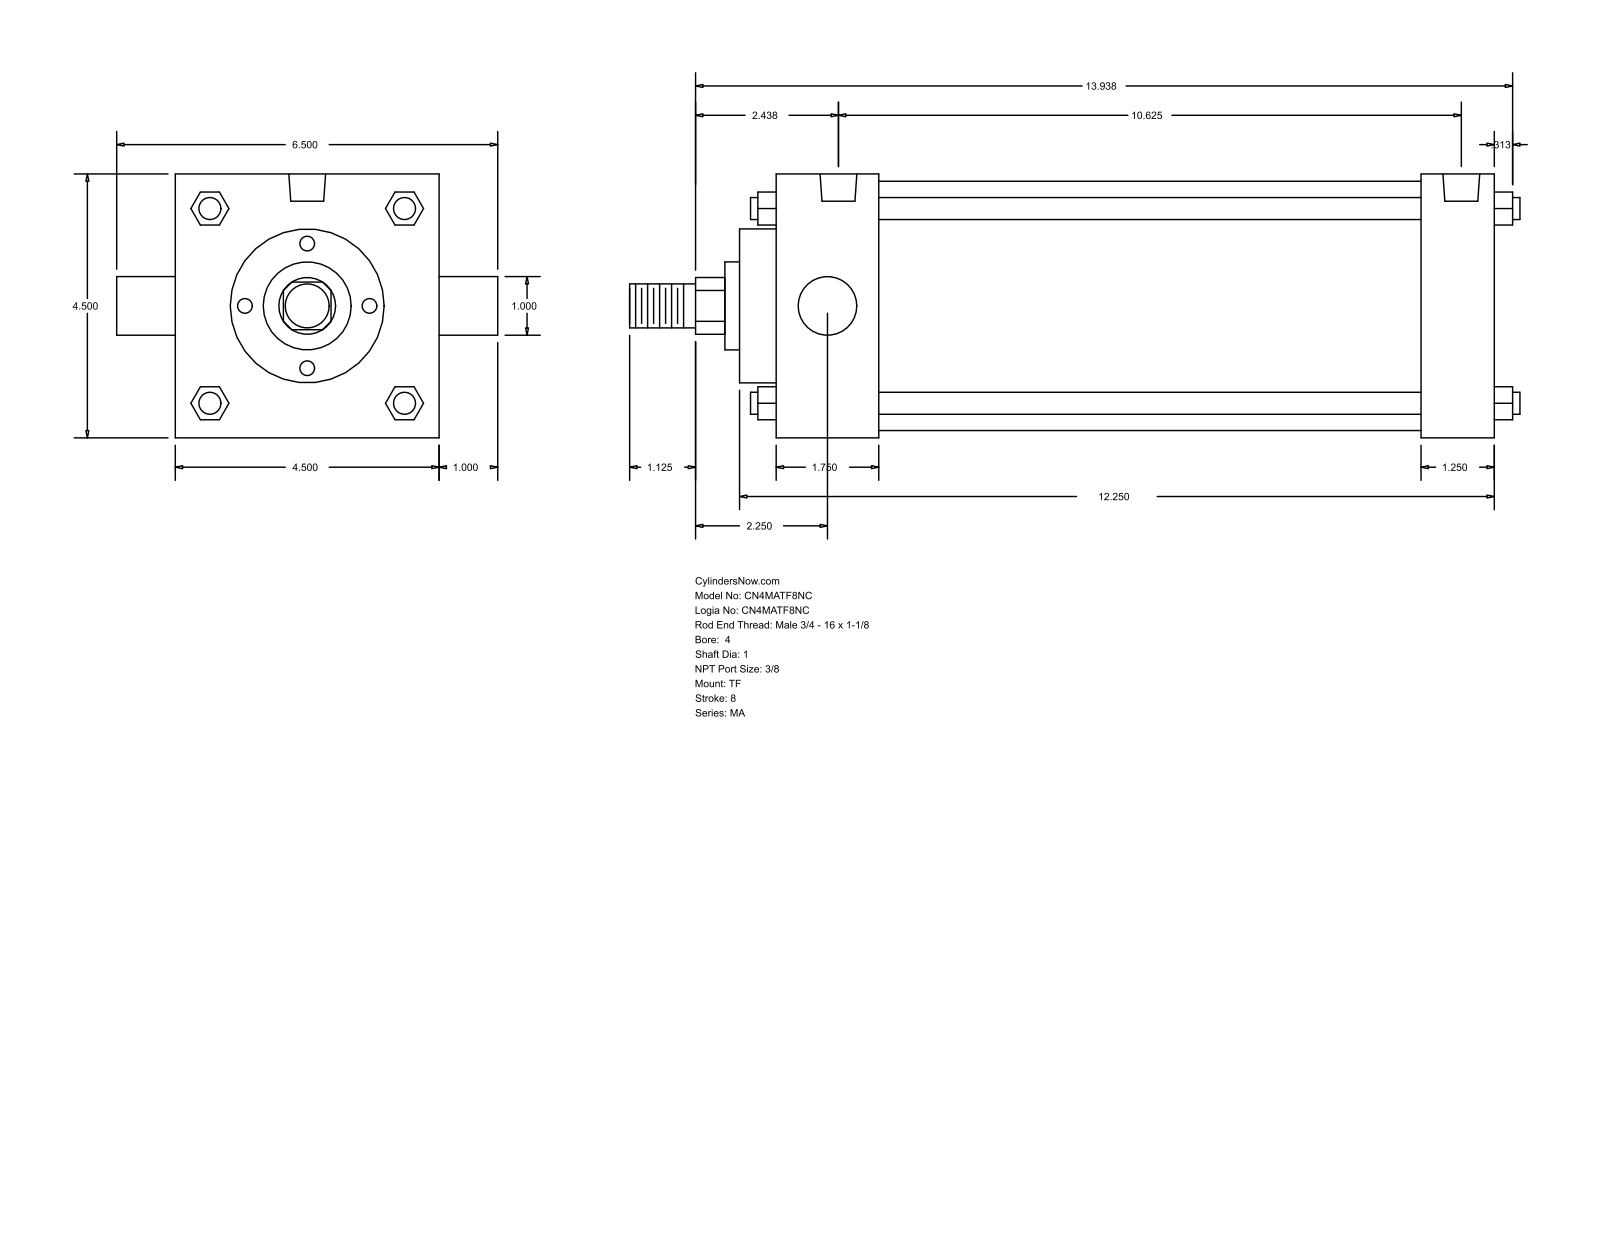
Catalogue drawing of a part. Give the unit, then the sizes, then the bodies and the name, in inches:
Units: inches
Overall size (bounding box): 15.187 × 6.5 × 4.5
Round holes (diameter × count): ⌀0.437 ×3, ⌀0.627 ×2
Round bosses / shafts (diameter × count): ⌀0.375 ×4, ⌀1 ×2, ⌀4.25 ×1, ⌀2.625 ×1, ⌀1.5 ×1, ⌀0.75 ×1
Partial cylindrical surfaces — rounded edges, fillets, slot ends (radius × count): R0.484 ×1
Main face-to-face distances: 4.5, 12.25, 11, 1.25, 1.75, 9.25, 10.5, 12.875, 0.625, 2.375
Hole centre spacings: 0.187, 0.188, 10.25, 10.437, 10.438, 10.625
Bodies: 0 solids, 122 faces (93 planar, 29 cylindrical, 0 other)
Part name (STEP PRODUCT): MA_TF__0400_1
STEP written by: GSSL Pune (CONFIG_CONTROL_DESIGN)
